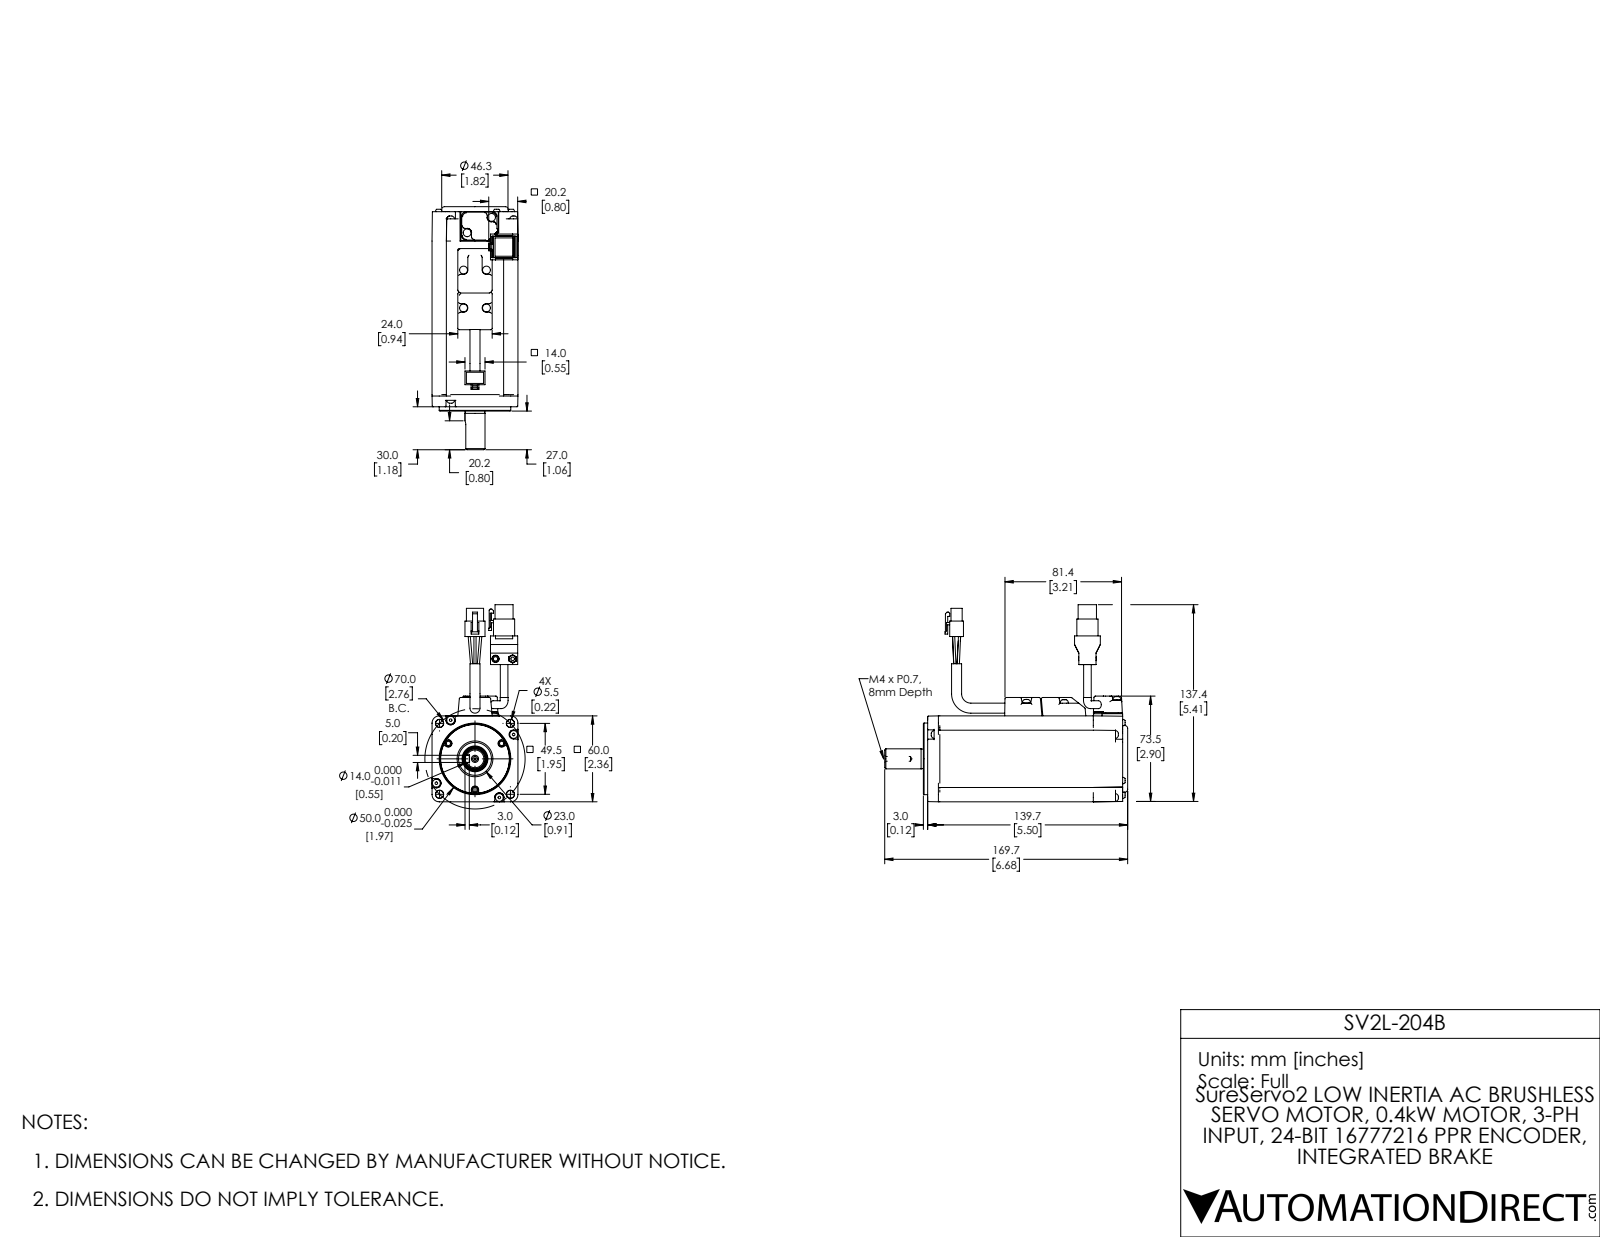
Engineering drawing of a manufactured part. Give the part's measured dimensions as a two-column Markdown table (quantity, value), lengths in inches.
| quantity | value |
| --- | --- |
| part name | SV2L-204B |
| STEP written by | SolidWorks 2021 (AUTOMOTIVE_DESIGN) |
| units | inches |
| bodies | 4 solids, 802 faces (330 planar, 260 cylindrical, 212 other) |
| overall size | 6.681 × 5.419 × 2.363 |
| volume | 29.74 in³ |
| surface area | 82.36 in² |
| round holes (diameter × count) | 0.201 × 2, 0.13 × 1, 0.906 × 1, 0.984 × 1 |
| round bosses / shafts (diameter × count) | 0.217 × 8, 0.059 × 6, 0.098 × 4, 0.276 × 2, 0.181 × 2, 0.169 × 2, 0.142 × 2, 1.969 × 1 |
| partial cylindrical surfaces (radius × count) | 0.039 × 52, 0.079 × 28, 0.02 × 24, 0.118 × 16, 0.03 × 5, 0.085 × 3, 0.087 × 3, 0.1 × 3 |
| main face-to-face distances | 2.362, 0.394, 1.969, 2.363, 0.118, 1.575, 5.618, 0.138, 5.48, 5.5 |
| hole center spacings | 0.472, 2.806, 2.938 |
